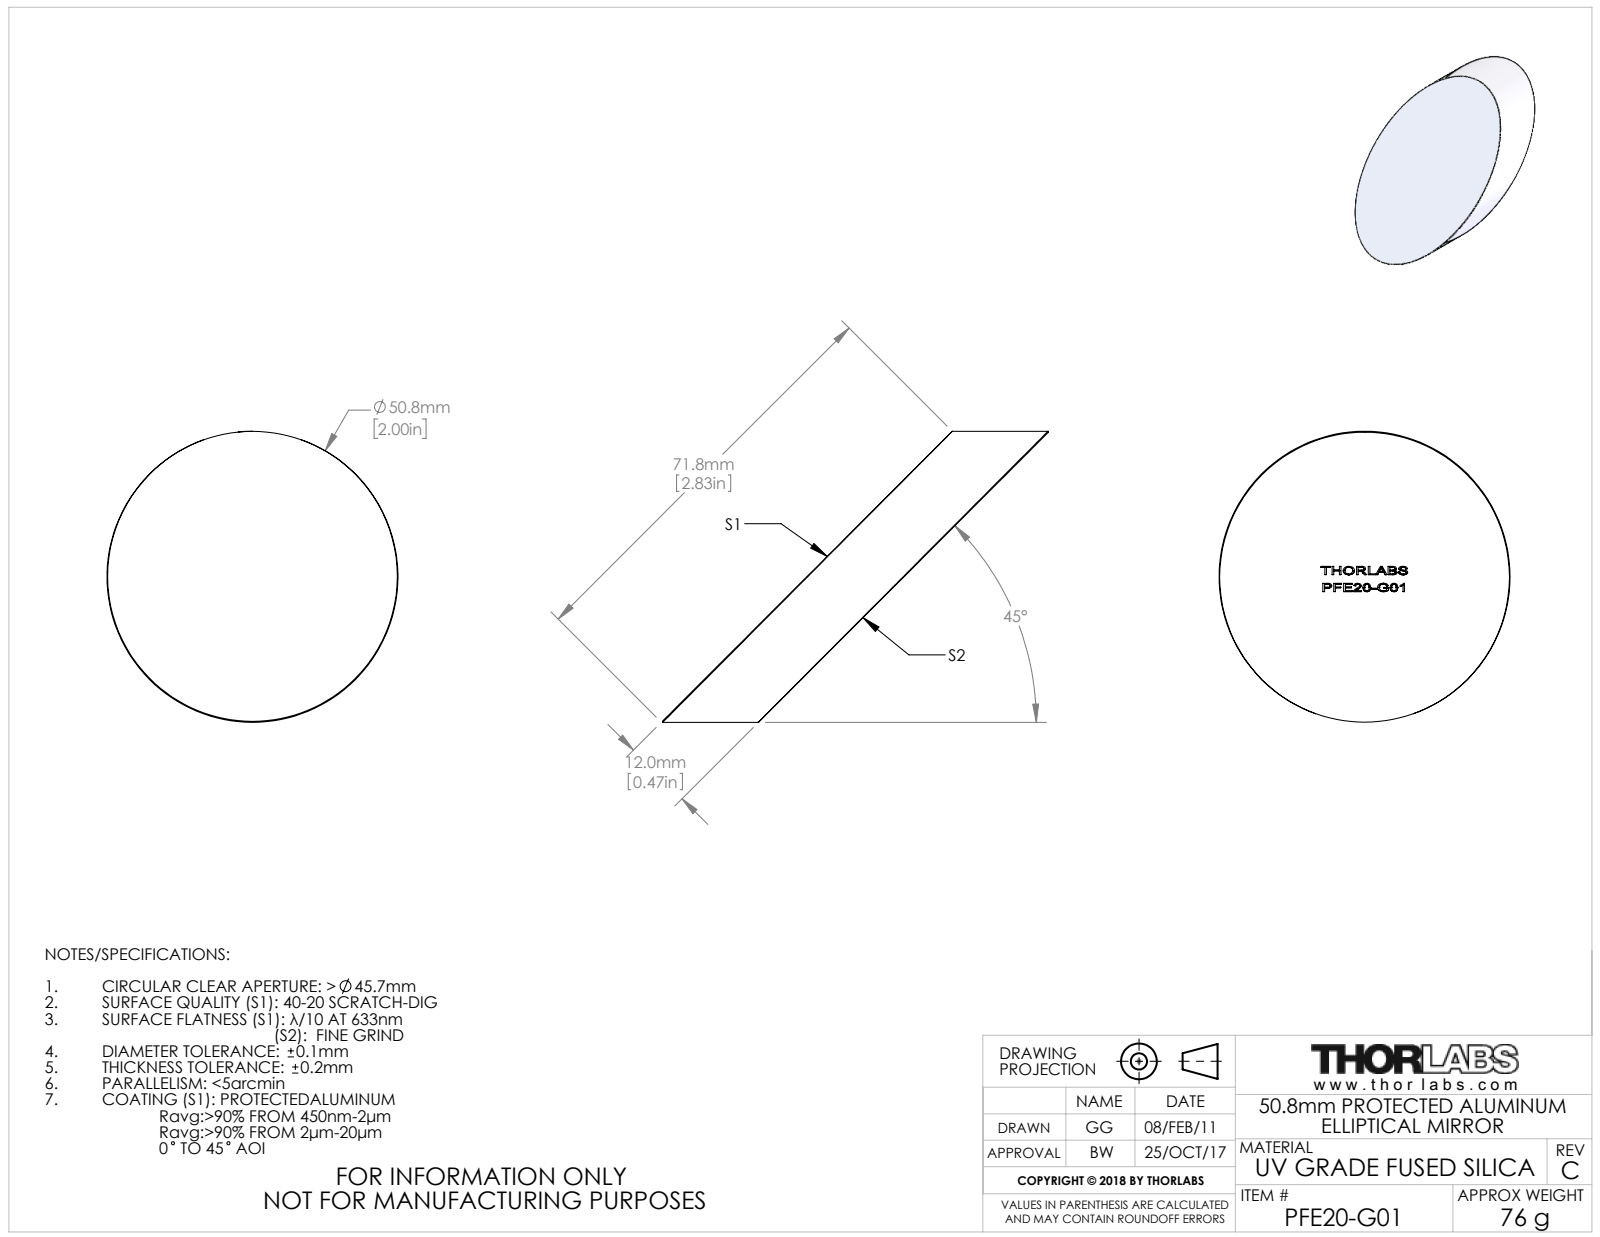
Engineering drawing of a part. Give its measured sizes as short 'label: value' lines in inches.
name: 21937-E0W
written by: SolidWorks 2016 (CONFIG_CONTROL_DESIGN)
unit: in
bodies: 1 solid, 229 faces (135 planar, 2 cylindrical, 92 other)
size: 2.654 × 2 × 2
volume: 2.099 in³; area: 13.02 in²
bosses: 1× ⌀2
face distances: 0.472, 0.164, 0.081, 0.218, 0.249, 0.117, 0.072, 0.062, 0.039, 0.169
